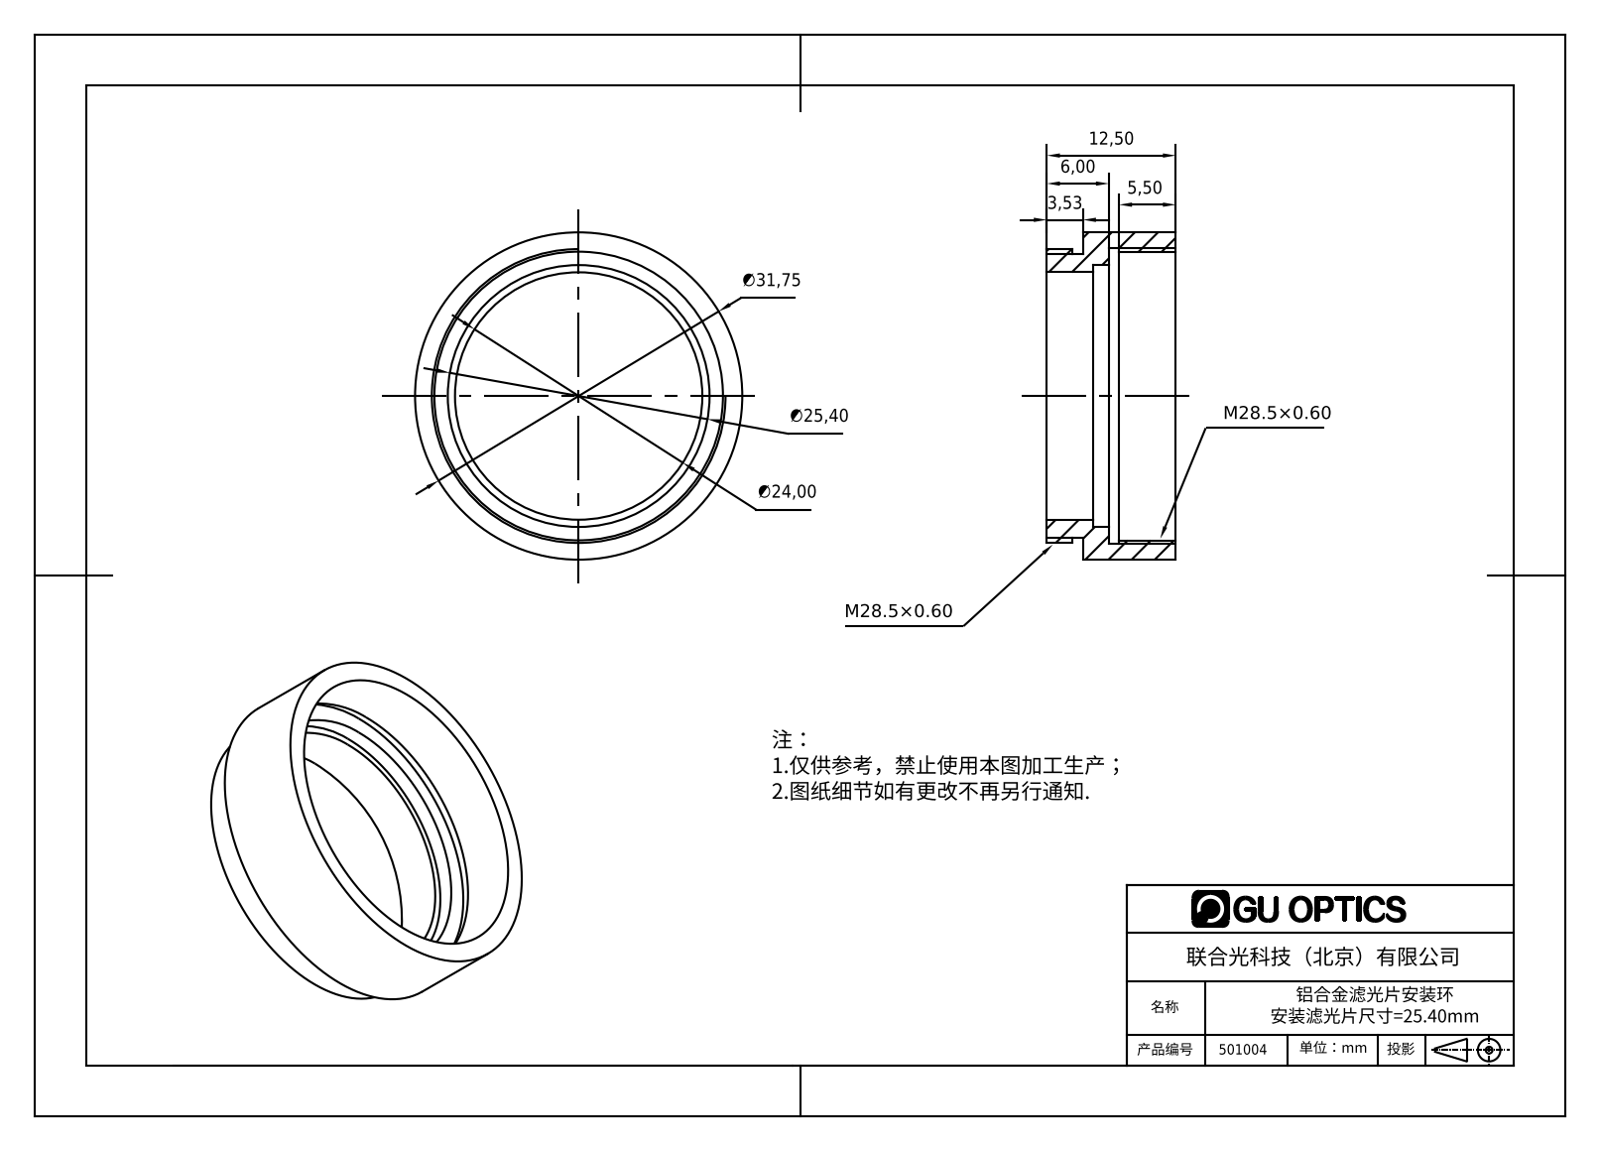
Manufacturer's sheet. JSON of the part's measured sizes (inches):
{"part_name": "501004", "step_written_by": "SolidWorks 2016 (CONFIG_CONTROL_DESIGN)", "units": "inches", "bodies": {"solids": 1, "faces": 21, "planar": 7, "cylindrical": 14, "other": 0}, "overall_size": [1.25, 1.25, 0.492], "volume_in3": 0.152, "surface_area_in2": 4.759, "round_holes": [[0.945, 1], [1, 1], [1.102, 1], [1.13, 1]], "round_bosses_or_shafts": [[1.25, 1], [1.122, 1], [1.083, 1]], "face_to_face_distances": [0.138, 0.098, 0.492, 0.354, 0.236, 0.256, 0.039, 0.177, 0.059, 0.315]}
